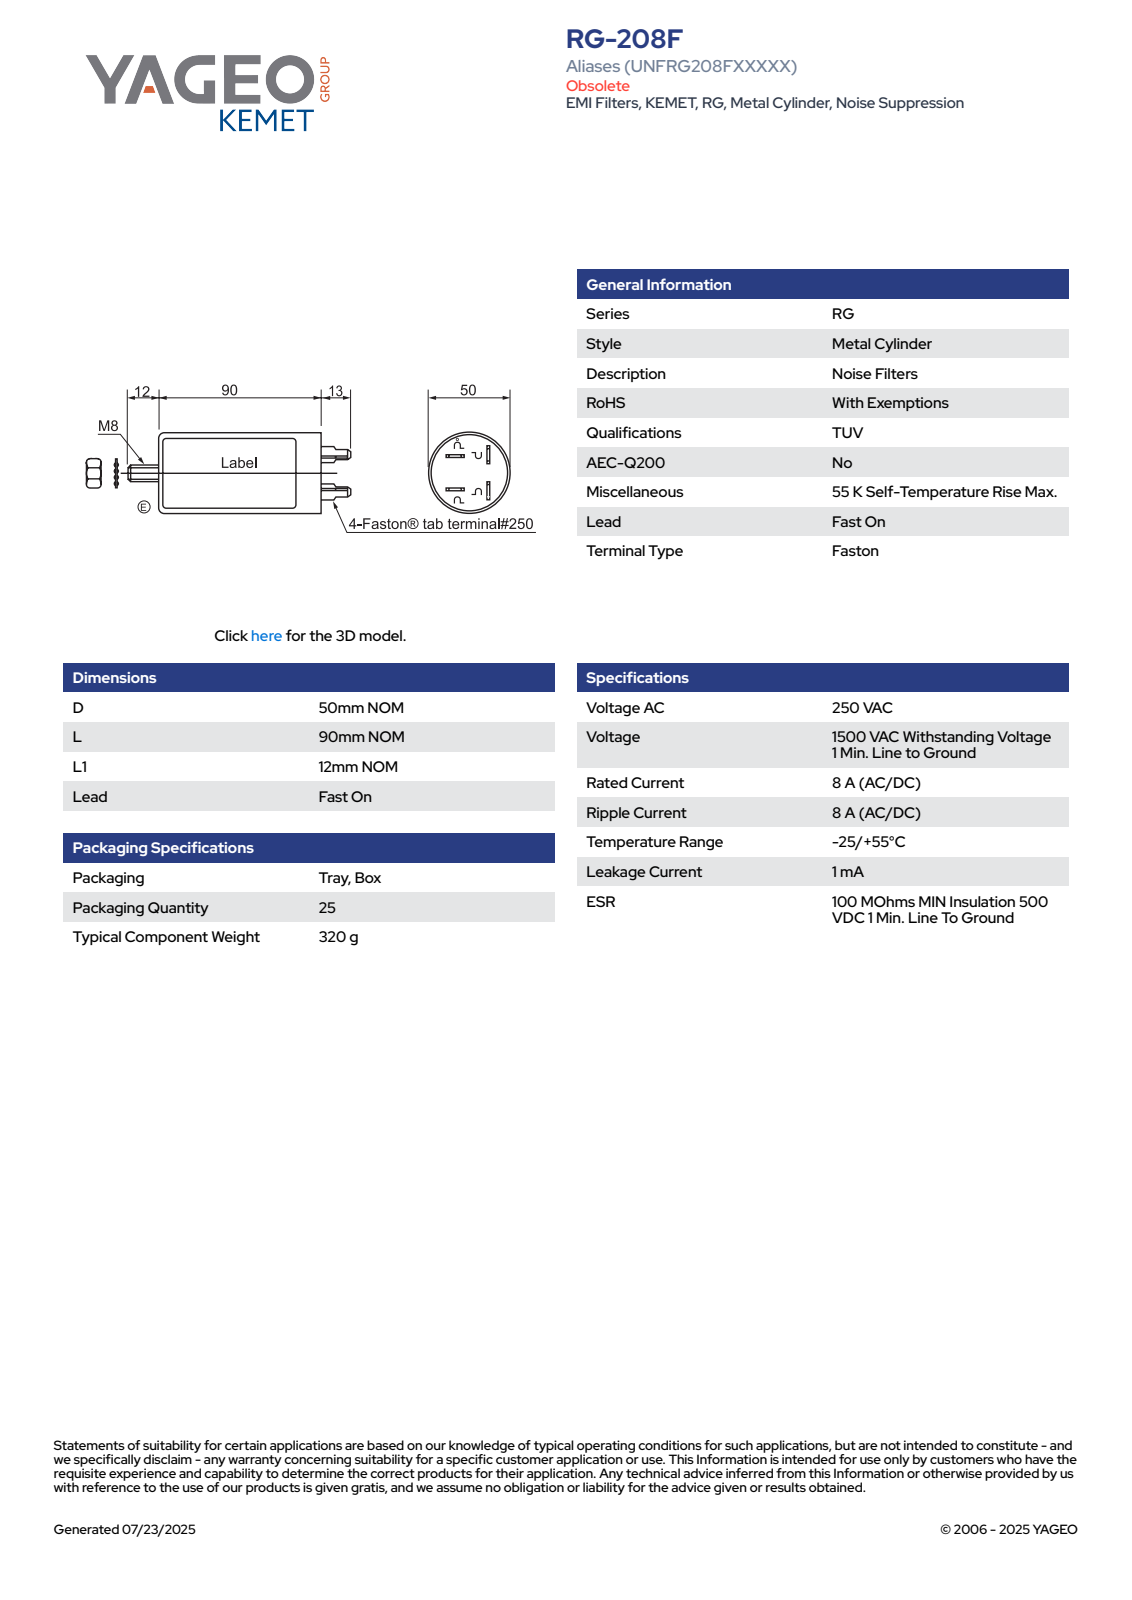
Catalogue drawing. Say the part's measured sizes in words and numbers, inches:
The part is named "Default". Its 3-D file was written by "SolidWorks 2014 (AUTOMOTIVE_DESIGN)". It is 1 solid with 140 faces: 61 planar, 44 cylindrical and 35 other. Overall it measures 4.528 by 1.969 by 1.969 inches. Its volume is 10.86 cubic inches and its surface area 29.86 square inches. Round holes: 3 of diameter 0.043. Round bosses or shafts: 1 of diameter 1.969, 1 of diameter 0.315. Partial cylindrical surfaces (rounded edges, fillets, slot ends): 18 of radius 0.02, 1 of radius 0.984. The main face-to-face distances are 3.543, 0.059, 0.571, 0.512, 0.63, 0.472, 4.016, 4.528, 4.055, 0.669. The hole center spacings are 0.669.
